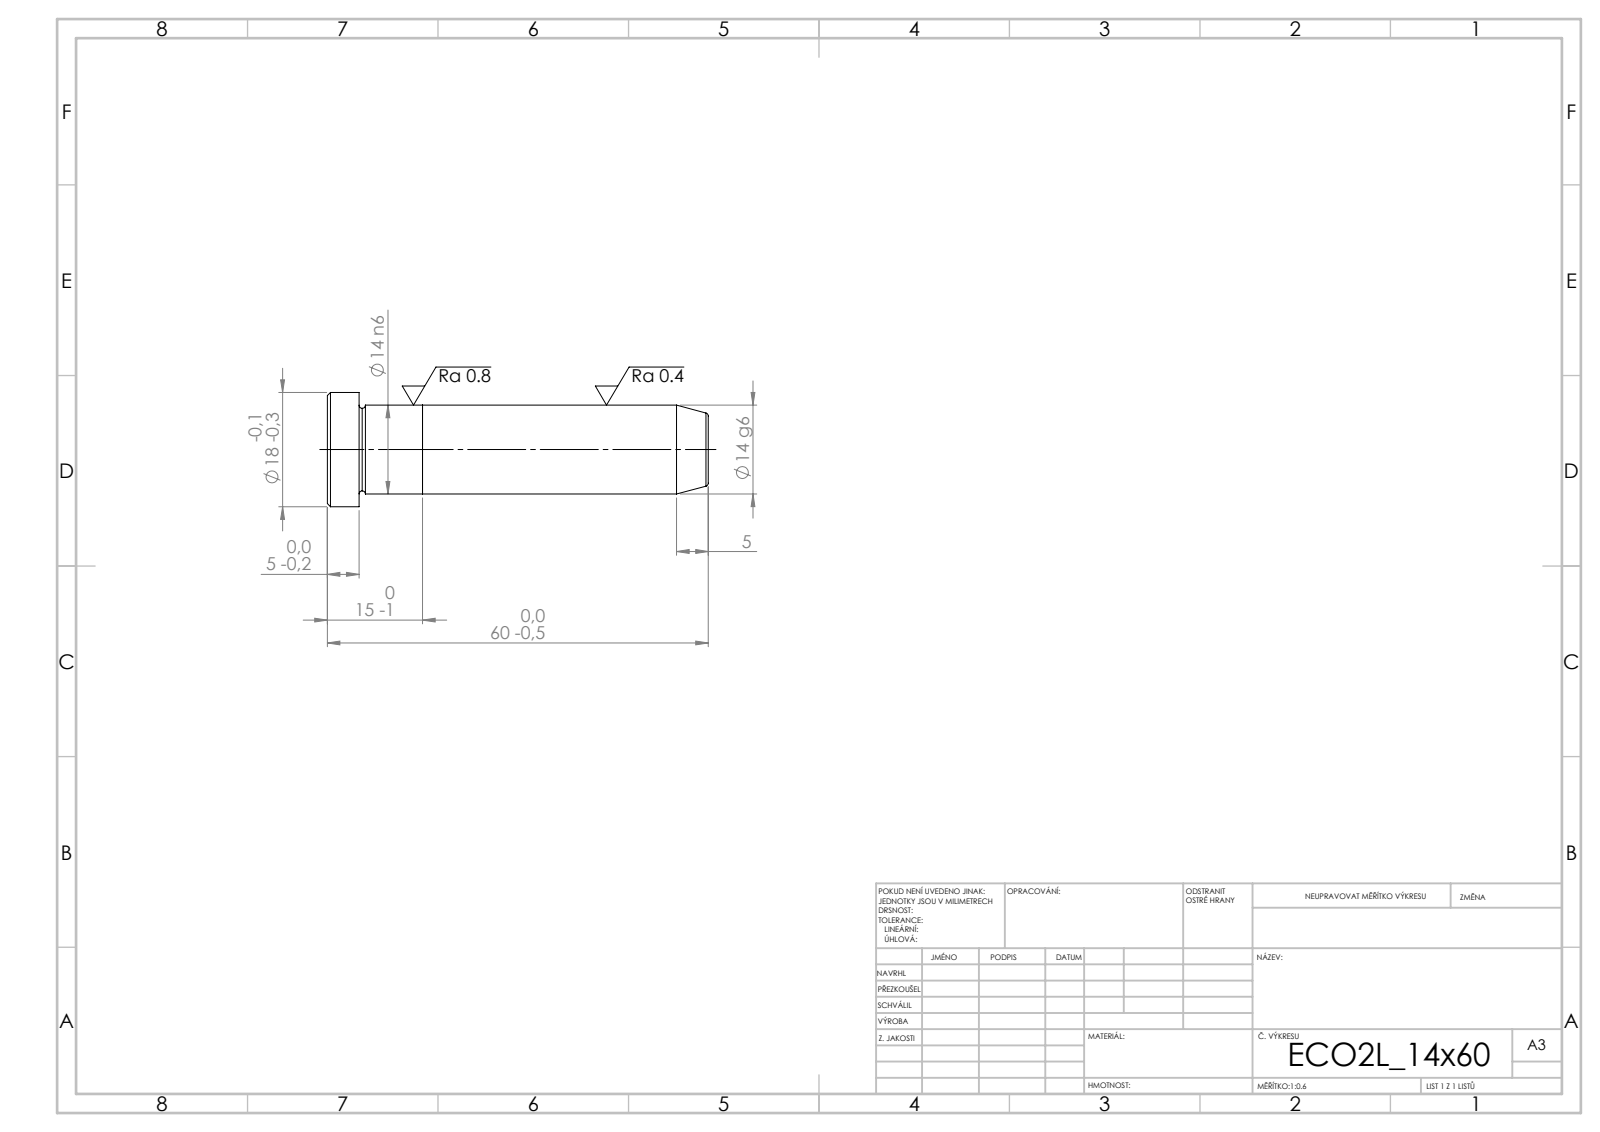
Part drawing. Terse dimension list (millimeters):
written by: SolidWorks 2019 (CONFIG_CONTROL_DESIGN)
unit: mm
bodies: 2 solids, 21 faces (5 planar, 6 cylindrical, 10 other)
size: 60 × 18 × 18
volume: 9 576 mm³; area: 3 452 mm²
bosses: 1× ⌀18, 1× ⌀14
face distances: 15, 10, 5, 45, 55, 60
